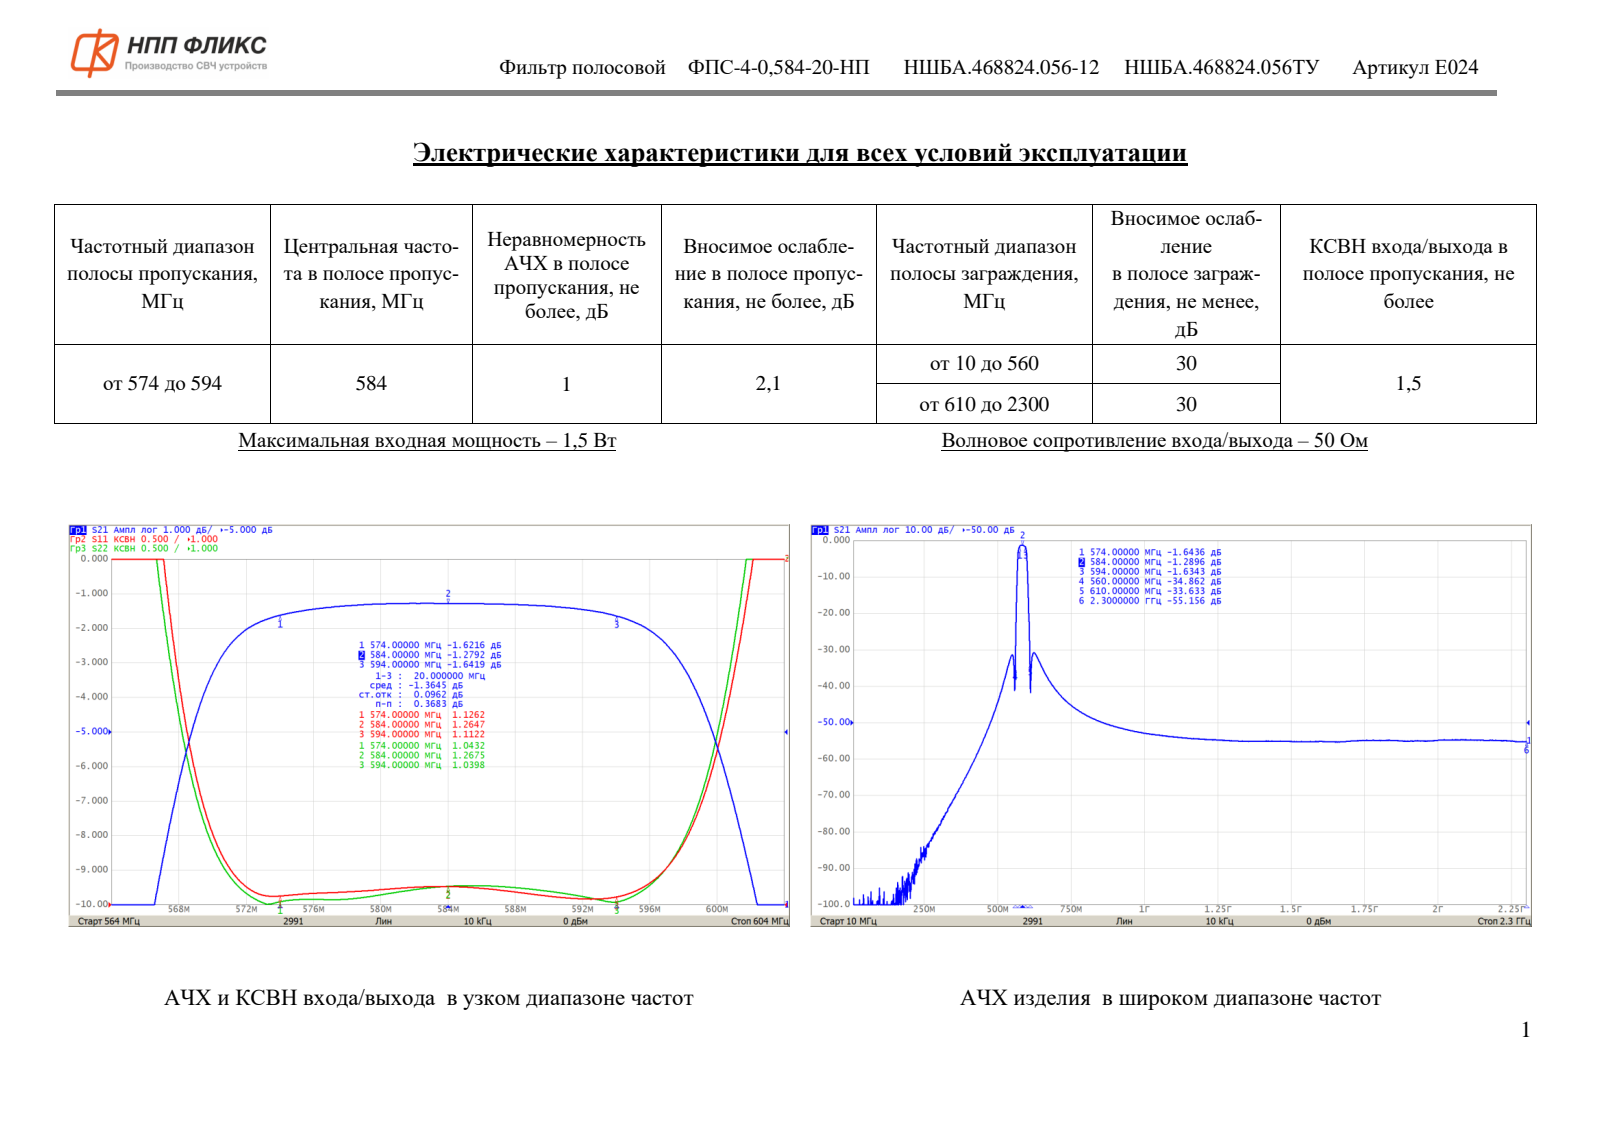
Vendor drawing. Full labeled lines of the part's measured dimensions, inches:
Part name (STEP PRODUCT): НШБА.468824.056-12_Фильтр ФПС-4-0,584-20-НП
STEP written by: ASCON Math Kernel (CONFIG_CONTROL_DESIGN)
Units: inches
Bodies: 1 solid, 782 faces (575 planar, 89 cylindrical, 118 other)
Overall size (bounding box): 1.181 × 0.984 × 0.666
Volume: 0.078 in³ · Surface area: 9.506 in²
Round holes (diameter × count): ⌀0.031 ×4, ⌀0.02 ×2
Partial cylindrical surfaces — rounded edges, fillets, slot ends (radius × count): R0.02 ×27, R0.012 ×8, R0.018 ×8, R0.024 ×8, R0.039 ×8, R0.01 ×1, R0.03 ×1, R0.035 ×1
Main face-to-face distances: 0.894, 0.032, 1.102, 0.666, 0.634, 0.654, 0.622, 0.882, 0.906, 1.091
Hole centre spacings: 0.463, 1.049, 0.827, 0.894, 1.217, 1.071
